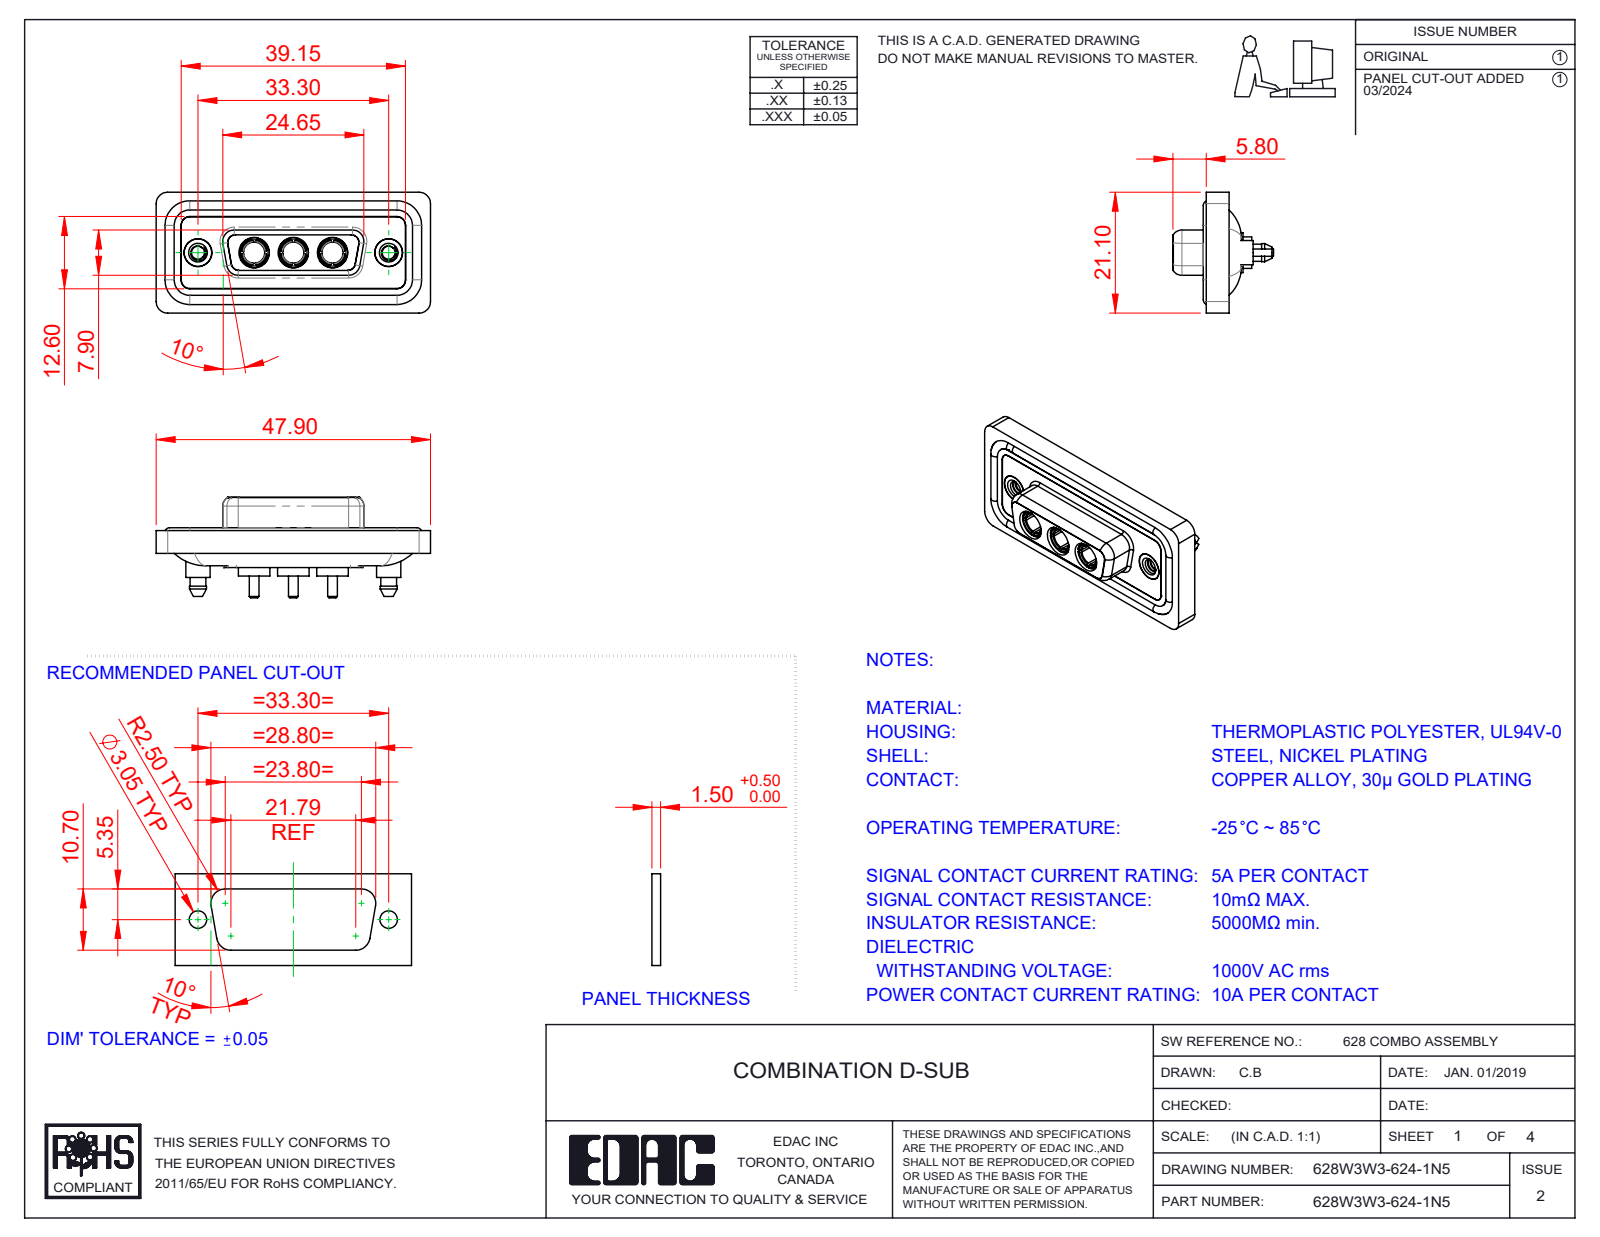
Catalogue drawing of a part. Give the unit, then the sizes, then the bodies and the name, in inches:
Units: inches
Overall size (bounding box): 1.886 × 0.831 × 0.691
Round holes (diameter × count): ⌀0.191 ×5, ⌀0.146 ×3, ⌀0.209 ×3, ⌀0.089 ×2, ⌀0.157 ×2, ⌀0.159 ×2, ⌀0.197 ×2
Round bosses / shafts (diameter × count): ⌀0.063 ×4, ⌀0.217 ×3, ⌀0.205 ×3, ⌀0.195 ×3, ⌀0.187 ×3, ⌀0.148 ×3, ⌀0.067 ×3, ⌀0.213 ×2
Partial cylindrical surfaces — rounded edges, fillets, slot ends (radius × count): R0.059 ×24, R0.079 ×20, R0.053 ×12, R0.063 ×10, R0.01 ×4, R0.02 ×4, R0.024 ×4, R0.026 ×4
Main face-to-face distances: 0.016, 0.071, 0.063, 0.02, 0.293, 0.043, 0.114, 0.222, 0.278, 0.059
Hole centre spacings: 0.27, 0.386, 0.656, 0.925, 0.539, 1.311
Volume: 0.373 in³ · Surface area: 15.55 in²
Bodies: 13 solids, 658 faces (208 planar, 289 cylindrical, 161 other)
Part name (STEP PRODUCT): 628Combo Shell Rear_15 Contacts; 628Combo Shell Front_15 Contacts; 628W3W3-624-1N5; 628Combo Housing_3W3 (+3 more)
STEP written by: SolidWorks 2023 (CONFIG_CONTROL_DESIGN)
